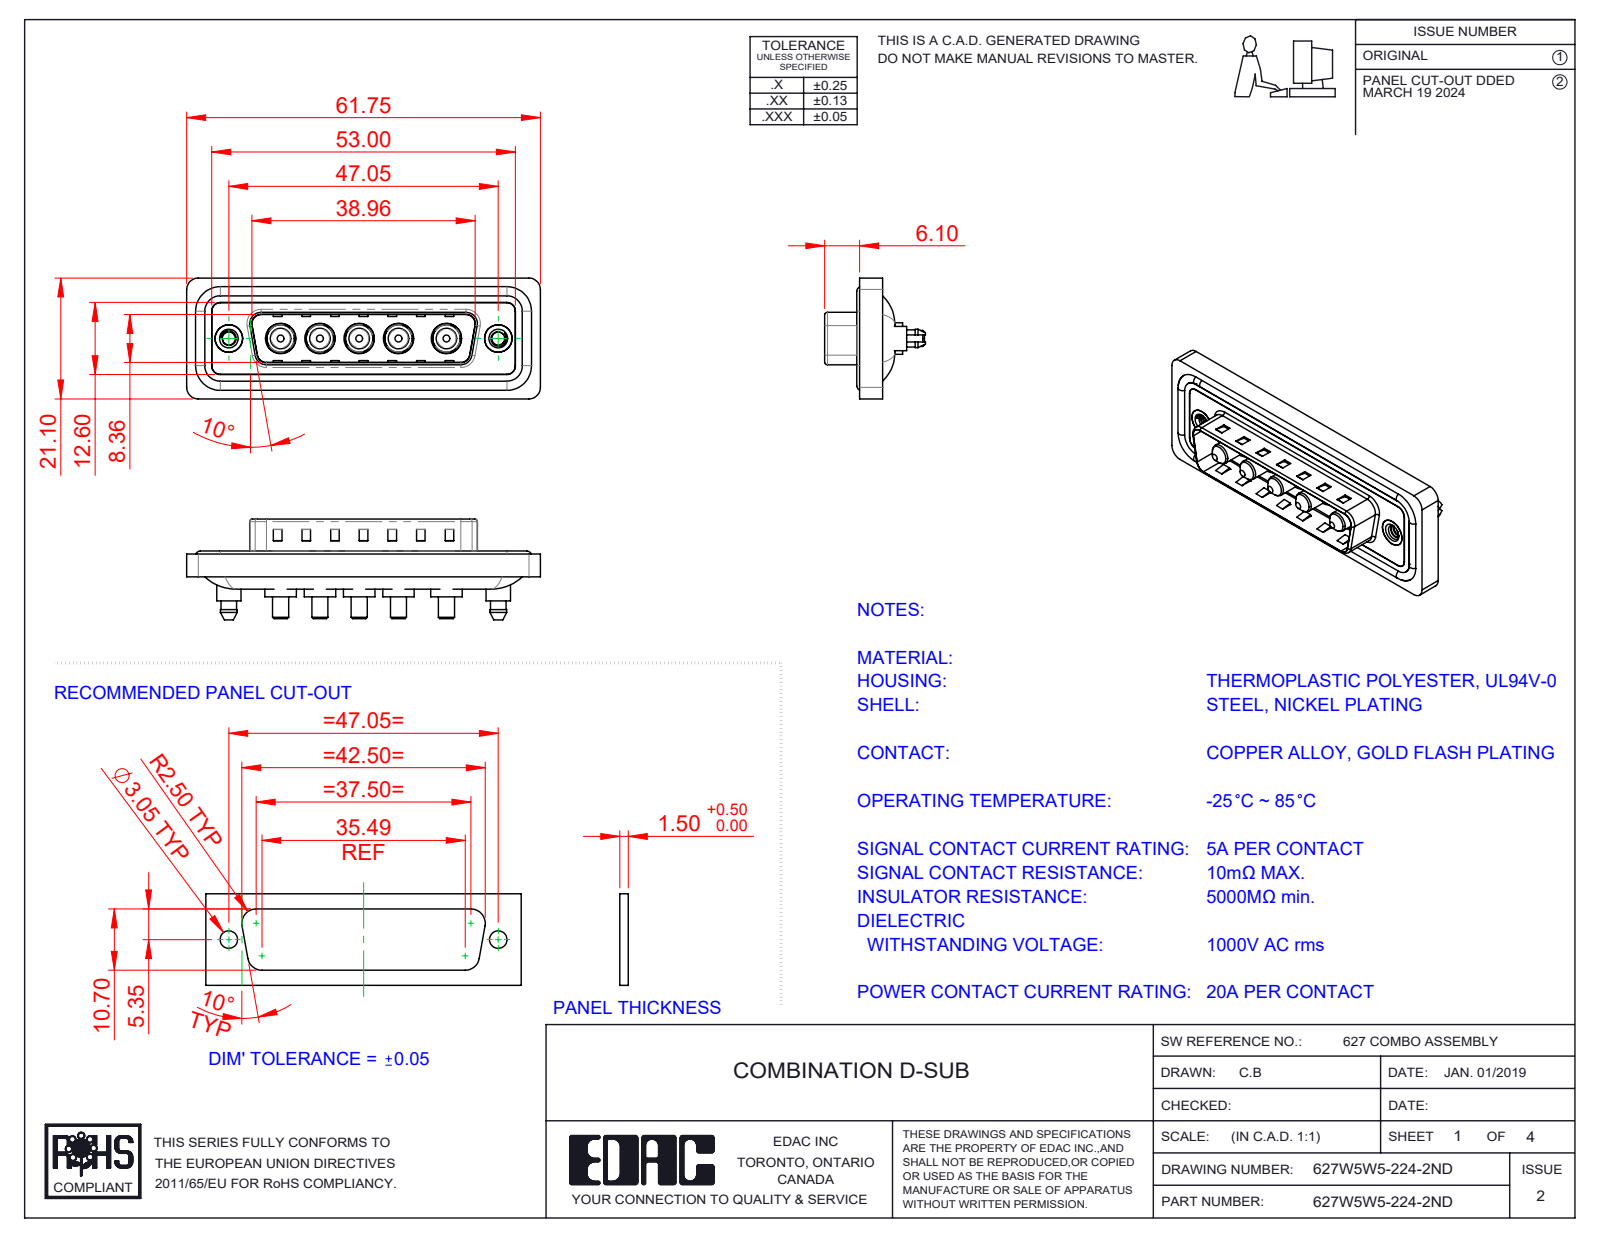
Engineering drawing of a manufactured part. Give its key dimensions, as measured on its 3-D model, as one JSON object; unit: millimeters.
{"part_name": "627Combo Waterproof Housing_25 Contacts; Power Pin_20A S; 627Combo Shell Front_25 Contacts; 627Combo Threaded Boardlock_5 (+4 more)", "step_written_by": "SolidWorks 2023 (CONFIG_CONTROL_DESIGN)", "units": "millimeters", "bodies": {"solids": 17, "faces": 736, "planar": 275, "cylindrical": 323, "other": 138}, "overall_size": [61.75, 21.1, 17.6], "volume_mm3": 7607, "surface_area_mm2": 12132, "round_holes": [[4.85, 5], [5.3, 5], [2.26, 2], [4, 2], [4.8, 2], [5, 2]], "round_bosses_or_shafts": [[5.5, 5], [5.2, 5], [4.75, 5], [3.75, 5], [3.6, 5], [2.8, 5], [1.6, 4], [5.4, 2]], "partial_cylinders_radius": [[1.5, 24], [2, 18], [1.6, 10], [0.5, 8], [2.1, 5], [0.25, 4], [0.6, 4], [0.65, 4]], "face_to_face_distances": [0.4, 1.5, 3.1, 1.1, 0.5, 1.6, 2.9, 0.82, 9.58, 5.65], "hole_center_spacings": [6.86, 9.04, 13.73, 38.01, 6.87, 8.37, 8.38, 9.05]}
